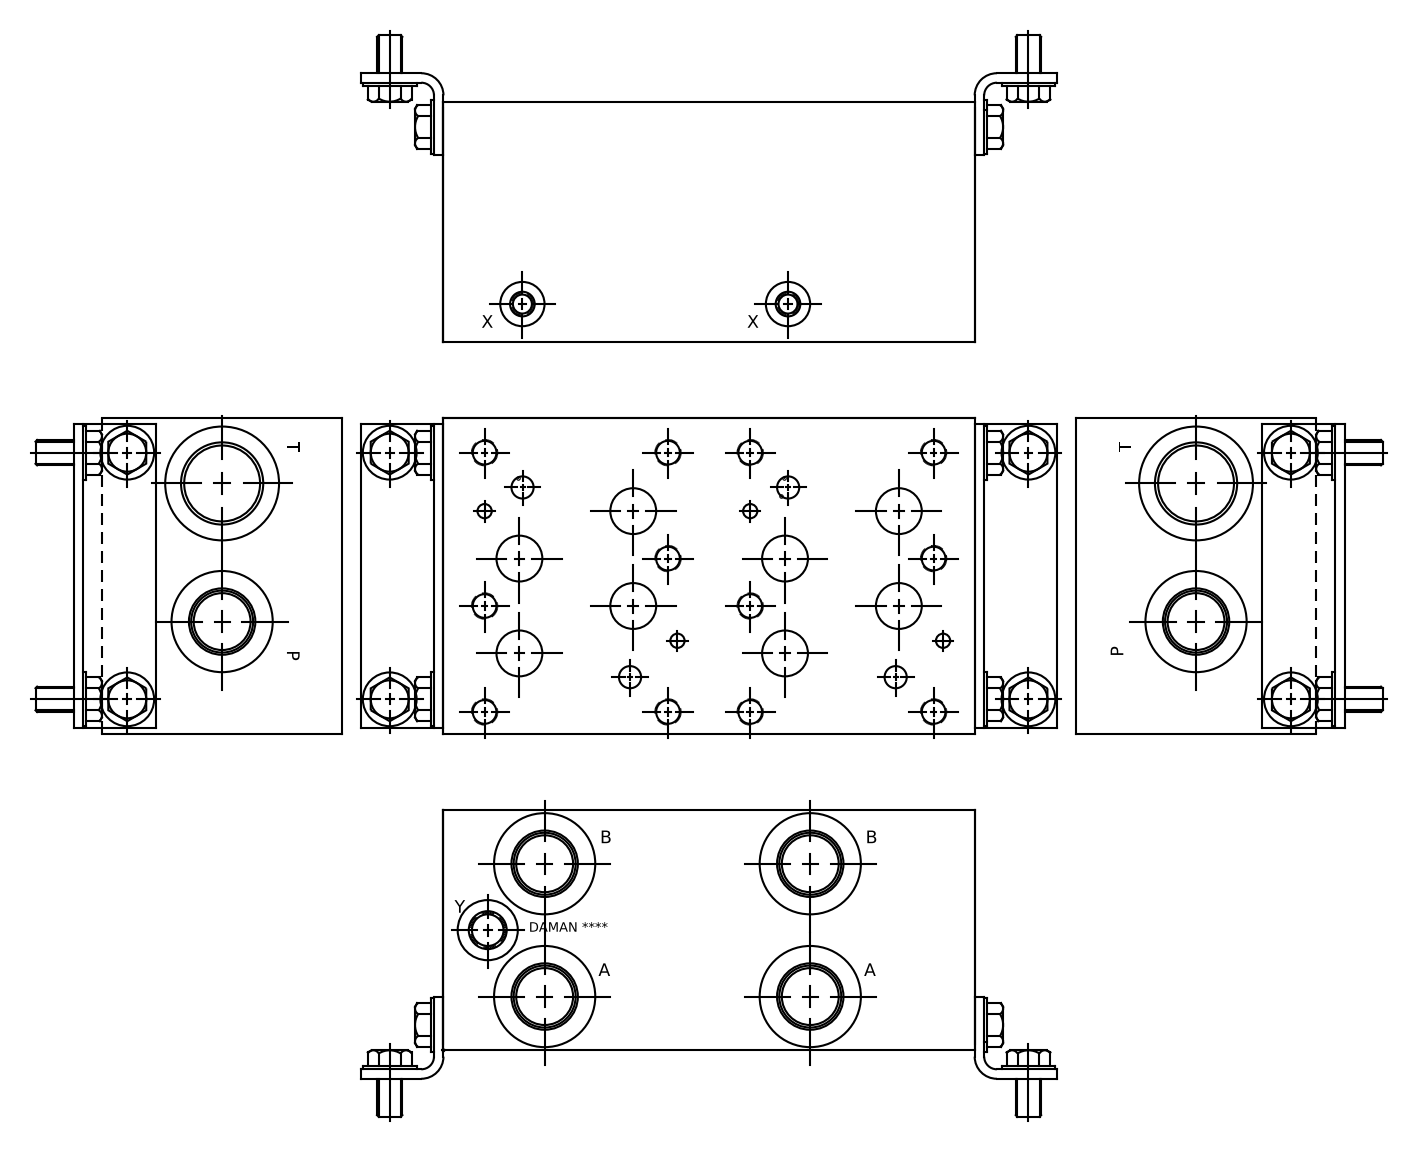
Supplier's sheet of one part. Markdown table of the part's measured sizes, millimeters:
| quantity | value |
| --- | --- |
| part name | C:\\\\Program Files\\\\PARO\\\\Hydroman 800\\\\Export\\\\AD08P025S_1PA_3D |
| STEP written by | Autodesk Inventor 2012 (AUTOMOTIVE_DESIGN) |
| units | millimeters |
| bodies | 1 solid, 158 faces (28 planar, 76 cylindrical, 54 other) |
| overall size | 266.7 × 158.75 × 120.65 |
| volume | 4 762 000 mm³ |
| surface area | 241 973 mm² |
| round holes (diameter × count) | 10.72 × 14, 23.01 × 6, 31.27 × 5, 35.51 × 5, 48.97 × 5, 7.14 × 4, 11.13 × 3, 9.53 × 2, 9.88 × 2, 12.4 × 2, 21.29 × 2, 23.02 × 2 |
| main face-to-face distances | 120.65, 158.75, 266.7, 0.79, 157.96, 265.91, 265.12, 4.06, 3.27, 262.64 |
| hole center spacings | 133.35, 29.54, 62.51, 76.99, 152.67, 159.45, 35.75, 61.92 |
